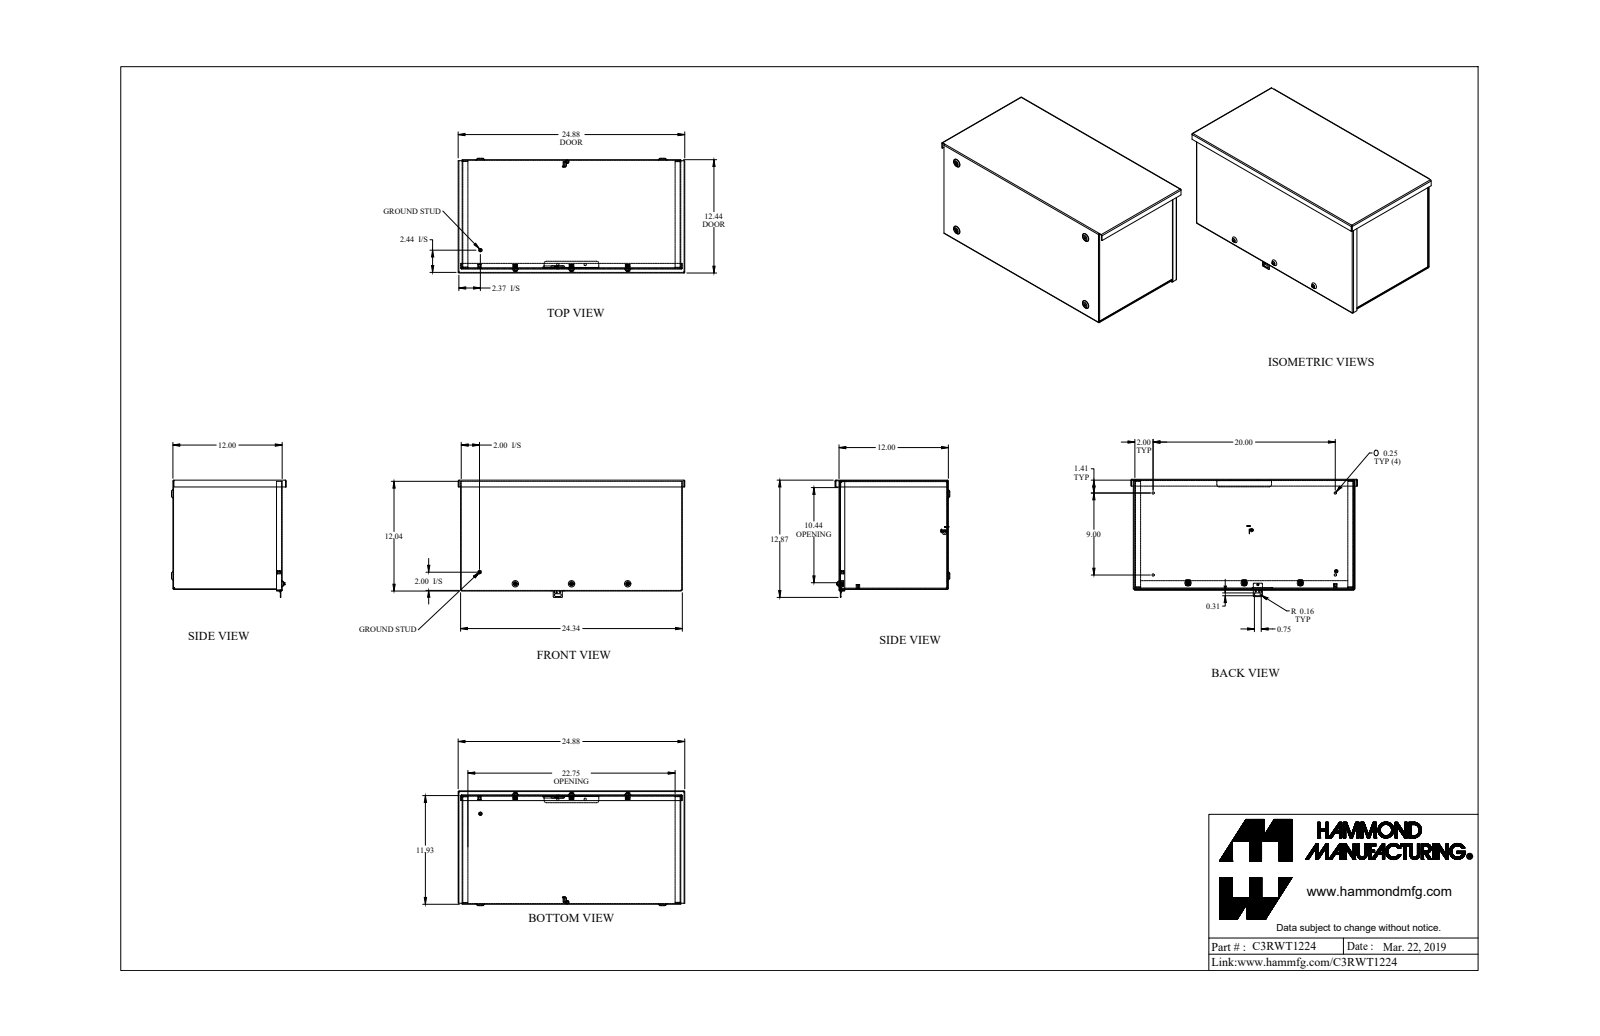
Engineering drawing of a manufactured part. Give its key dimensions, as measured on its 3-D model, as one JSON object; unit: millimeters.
{"part_name": "C3RWT1224_Default", "step_written_by": "SolidWorks 2019 (CONFIG_CONTROL_DESIGN)", "units": "millimeters", "bodies": {"solids": 22, "faces": 764, "planar": 415, "cylindrical": 237, "other": 112}, "overall_size": [631.8, 326.9, 319.9], "volume_mm3": 1876000, "surface_area_mm2": 2072000, "round_holes": [[6.4, 6], [4, 5], [5.4, 3], [5.8, 3], [5.2, 2], [3.2, 1], [3.5, 1], [5.1, 1], [5.5, 1]], "round_bosses_or_shafts": [[4.8, 4], [3.8, 3], [9.5, 2], [12.7, 1], [9.3, 1], [5.3, 1], [3.9, 1], [3.2, 1]], "partial_cylinders_radius": [[0.9, 18], [2.7, 18], [2, 12], [2.7, 12], [3.2, 11], [0.6, 6], [6.4, 6], [0.4, 4]], "face_to_face_distances": [1.8, 303, 301.1, 304.8, 607.8, 609.6, 605.9, 4.4, 300.6, 2.3], "hole_center_spacings": [156.8, 99.7, 144.3, 255, 313.5, 411.4, 435.2, 38.4]}
